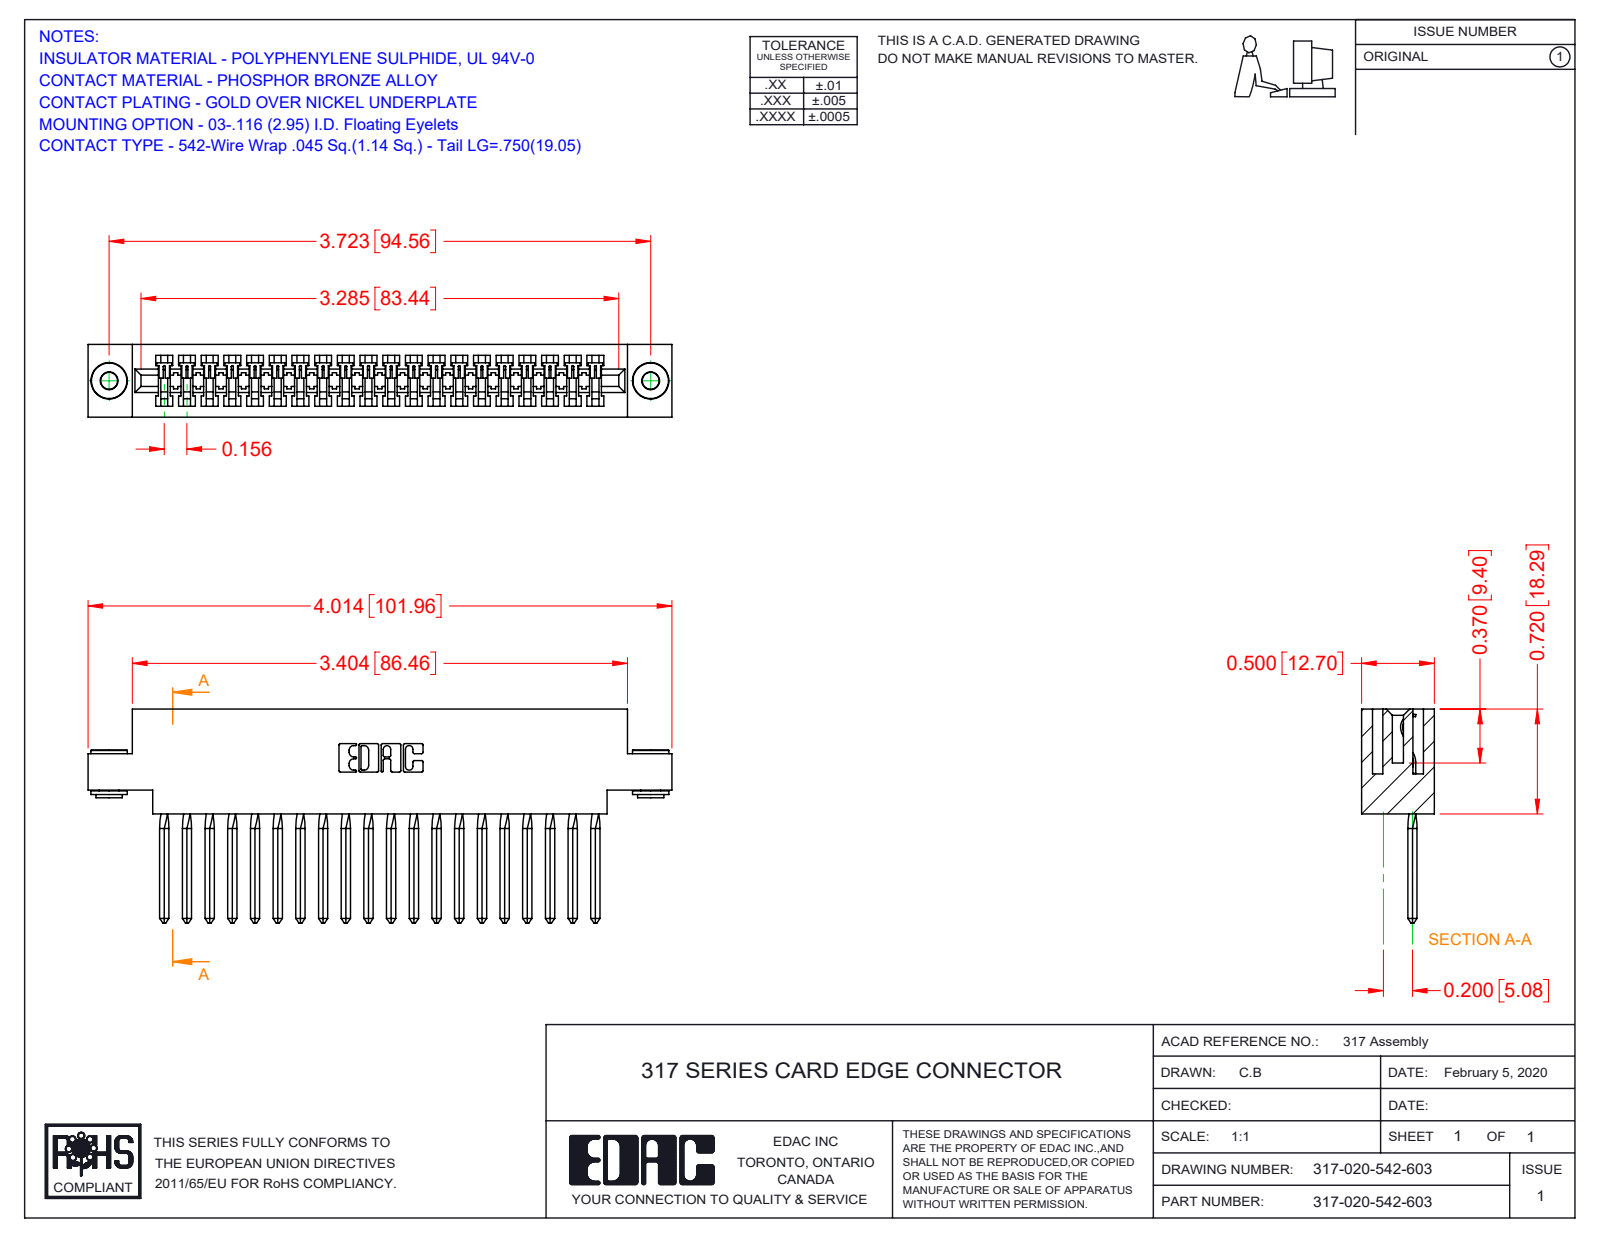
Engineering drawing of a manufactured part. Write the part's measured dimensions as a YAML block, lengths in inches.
part_name: "345-250-002_345-250-002-102; 317-020-542-603; 317-290-003_542; 317 Part_.156 Dia - TH"
step_written_by: "SolidWorks 2016 (CONFIG_CONTROL_DESIGN)"
units: inches
bodies: {solids: 23, faces: 1640, planar: 1348, cylindrical: 204, other: 88}
overall_size: [4.014, 1.47, 0.5]
volume: 0.927
surface_area: 28.29
round_holes:
  - {diameter: 0.116, count: 2}
  - {diameter: 0.156, count: 2}
round_bosses_or_shafts:
  - {diameter: 0.25, count: 2}
  - {diameter: 0.18, count: 2}
  - {diameter: 0.136, count: 2}
partial_cylinders:
  - {radius: 0.006, count: 40}
  - {radius: 0.01, count: 22}
  - {radius: 0.007, count: 6}
  - {radius: 0.031, count: 6}
  - {radius: 0.026, count: 3}
  - {radius: 0.074, count: 1}
  - {radius: 0.089, count: 1}
  - {radius: 0.1, count: 1}
face_to_face_distances: [0.5, 0.075, 0.425, 0.35, 0.11, 0.136, 0.72, 0.279, 0.772, 0.211]
hole_center_spacings: [3.723]
